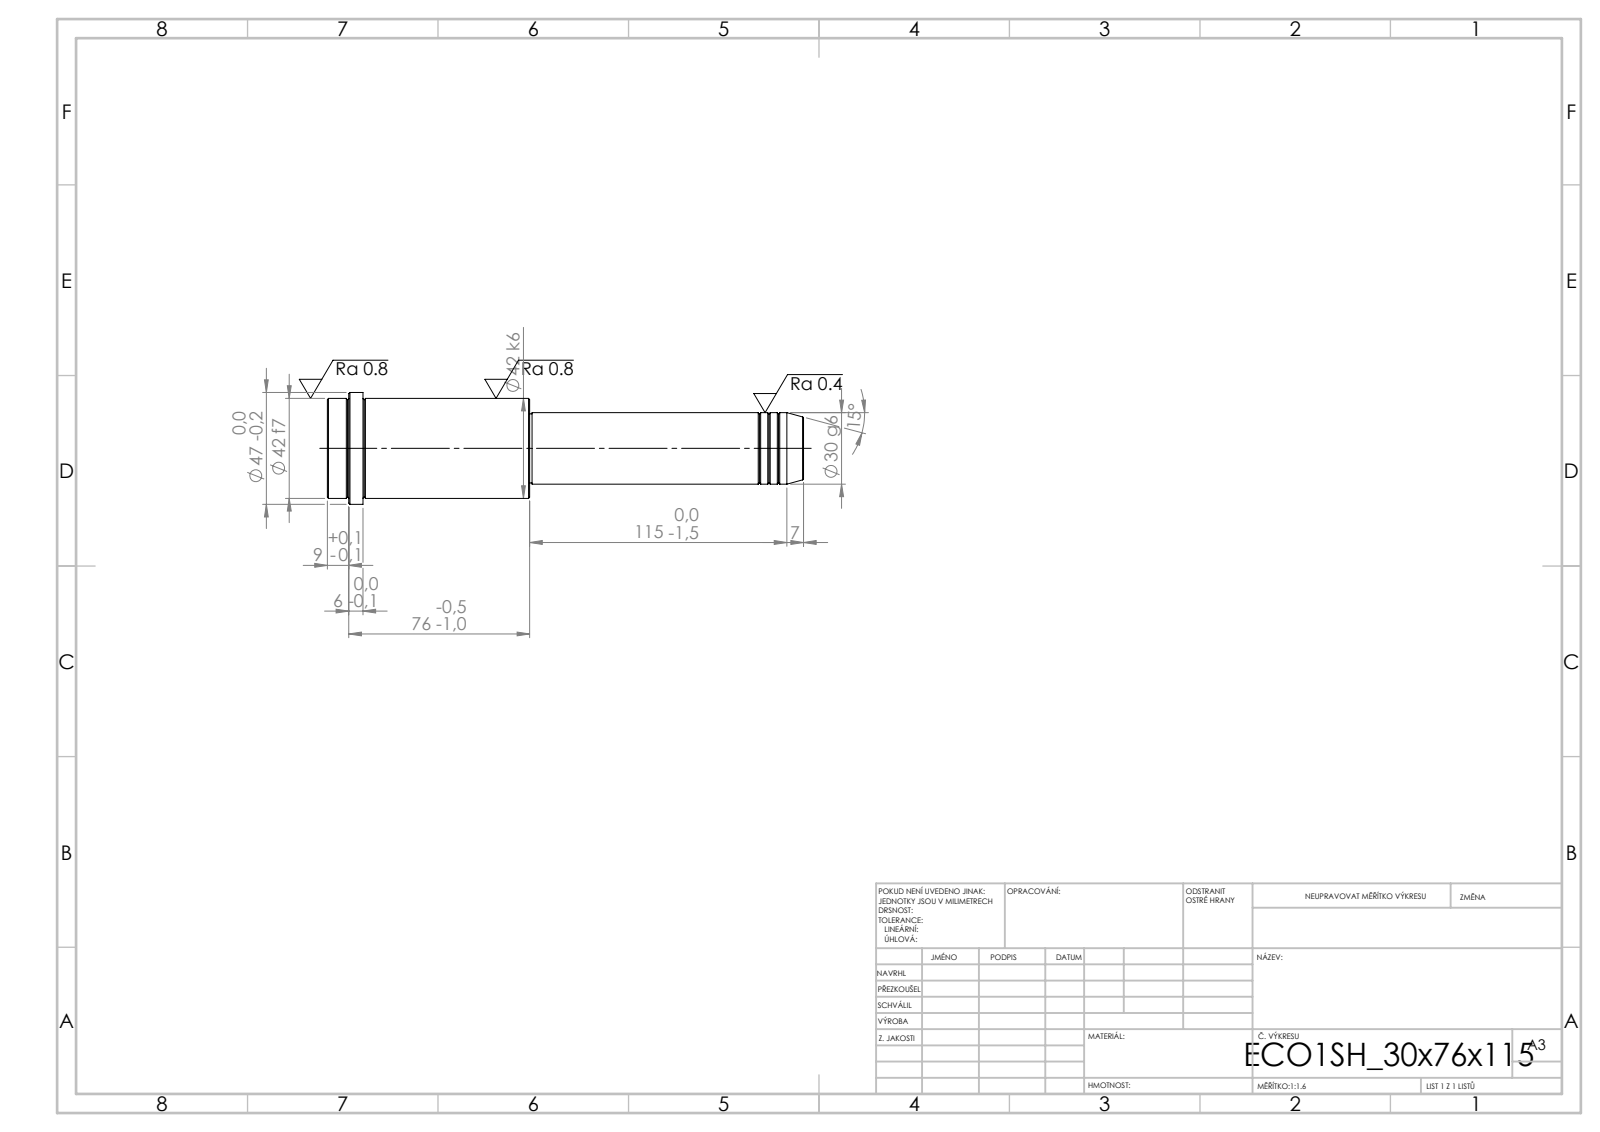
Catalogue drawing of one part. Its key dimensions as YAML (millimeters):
step_written_by: "SolidWorks 2019 (CONFIG_CONTROL_DESIGN)"
units: millimeters
bodies: {solids: 1, faces: 52, planar: 6, cylindrical: 16, other: 30}
overall_size: [200, 47, 47]
volume: 200244
surface_area: 25688
round_bosses_or_shafts:
  - {diameter: 47, count: 1}
  - {diameter: 42, count: 1}
  - {diameter: 30, count: 1}
  - {diameter: 29, count: 1}
face_to_face_distances: [85, 115, 200, 185, 70, 15, 191, 76, 6, 9]
